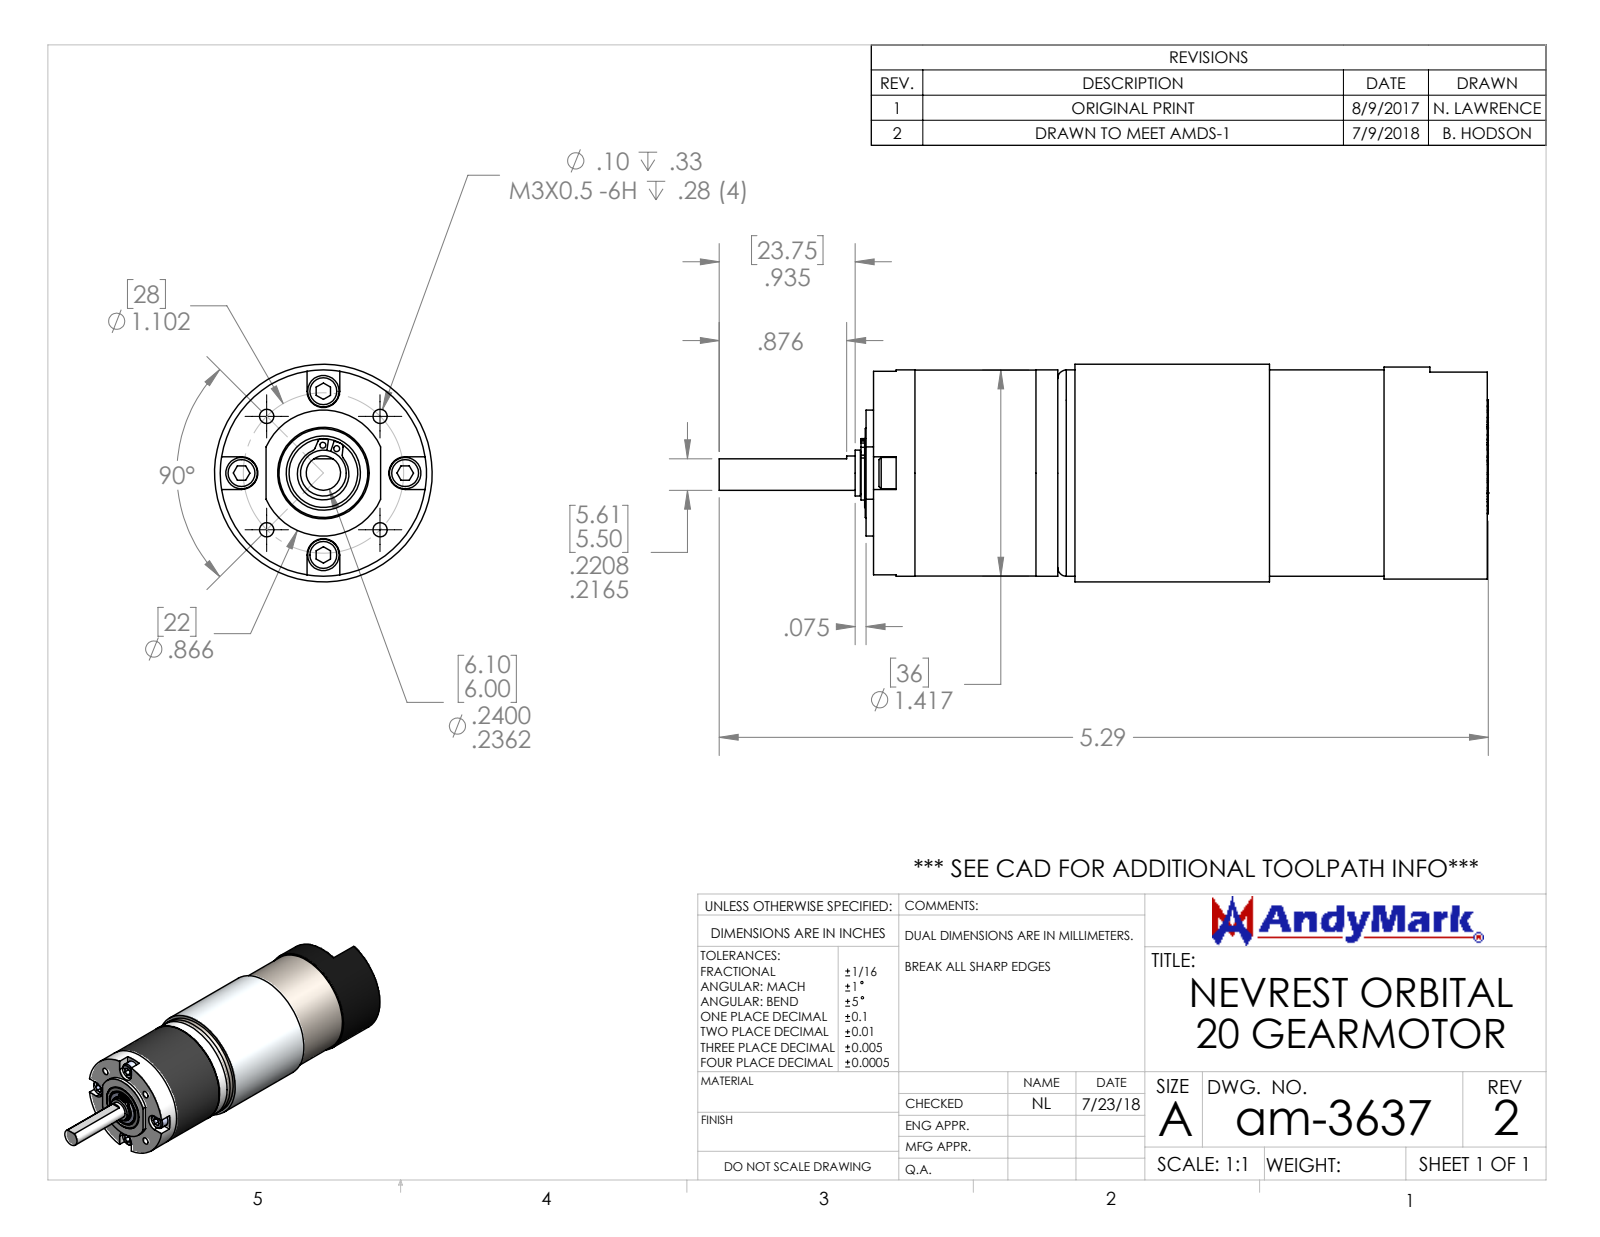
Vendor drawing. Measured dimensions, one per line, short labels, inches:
name: 7804K117_STAINLESS STEEL BALL BEARING_7804K117; SHCS M3 x 16mm; 97633A150_BLACK-FINISH STEEL EXTERNAL RETAINING RING_97633A150_grv; Shim (+3 more)
written by: SolidWorks 2021 (AUTOMOTIVE_DESIGN)
unit: in
bodies: 24 solids, 599 faces (268 planar, 125 cylindrical, 206 other)
size: 5.287 × 1.496 × 1.496
volume: 6.768 in³; area: 35.35 in²
holes: 10× ⌀0.098, 5× ⌀0.125, 2× ⌀0.041, 1× ⌀0.125, 1× ⌀0.29, 1× ⌀0.315, 1× ⌀0.434, 1× ⌀0.511, 1× ⌀0.512, 1× ⌀0.63
bosses: 4× ⌀0.217, 4× ⌀0.118, 1× ⌀1.496, 1× ⌀1.457, 1× ⌀1.417, 1× ⌀1.415, 1× ⌀0.472, 1× ⌀0.236
rounds: 4× R0.028, 3× R0.112, 1× R0.113, 1× R0.177, 1× R0.433
face distances: 2.952, 4.219, 1.266, 0.197, 0.394, 2.559, 3.825, 4.27, 3.876, 1.317
hole spacings: 0.426, 1.029, 0.409, 0.551, 0.78, 0.563, 0.739, 0.191
